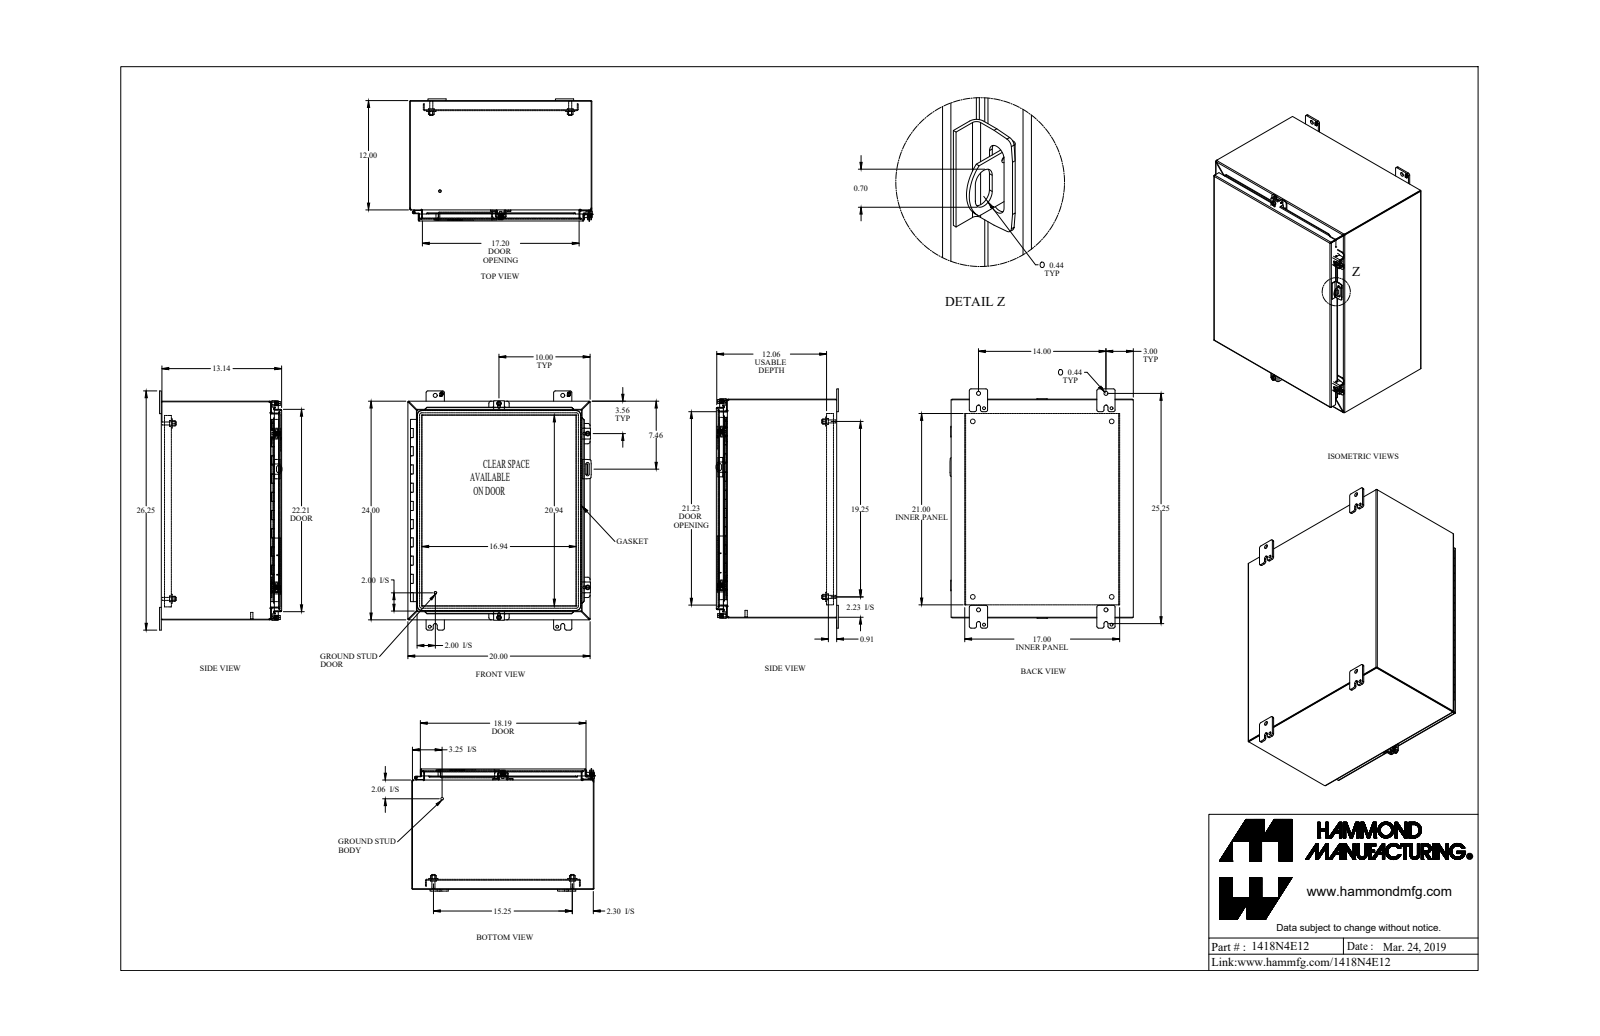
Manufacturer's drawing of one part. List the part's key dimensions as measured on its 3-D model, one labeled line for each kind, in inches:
Part name (STEP PRODUCT): 1418N4E12_Default
STEP written by: SolidWorks 2019 (CONFIG_CONTROL_DESIGN)
Units: inches
Bodies: 41 solids, 1407 faces (837 planar, 477 cylindrical, 93 other)
Overall size (bounding box): 26.25 × 20.126 × 13.437
Volume: 210.9 in³ · Surface area: 5 576 in²
Round holes (diameter × count): ⌀0.213 ×4, ⌀0.313 ×4, ⌀0.375 ×4, ⌀0.437 ×4, ⌀0.5 ×4, ⌀0.265 ×2, ⌀0.265 ×2, ⌀0.307 ×2, ⌀0.445 ×2, ⌀0.125 ×1, ⌀0.187 ×1
Round bosses / shafts (diameter × count): ⌀0.65 ×4, ⌀0.5 ×4, ⌀0.39 ×4, ⌀0.375 ×4, ⌀0.33 ×4, ⌀0.244 ×4, ⌀1 ×2, ⌀0.281 ×2
Partial cylindrical surfaces — rounded edges, fillets, slot ends (radius × count): R0.188 ×26, R0.25 ×24, R0.036 ×22, R0.108 ×22, R0.048 ×21, R0.143 ×21, R0.125 ×10, R0.04 ×8
Main face-to-face distances: 0.072, 19.928, 23.928, 13.066, 13.138, 0.072, 13.138, 13.21, 0.095, 12.106
Hole centre spacings: 14, 19.25, 24.559, 1.559, 3.135, 20.688, 22.331, 25.328
